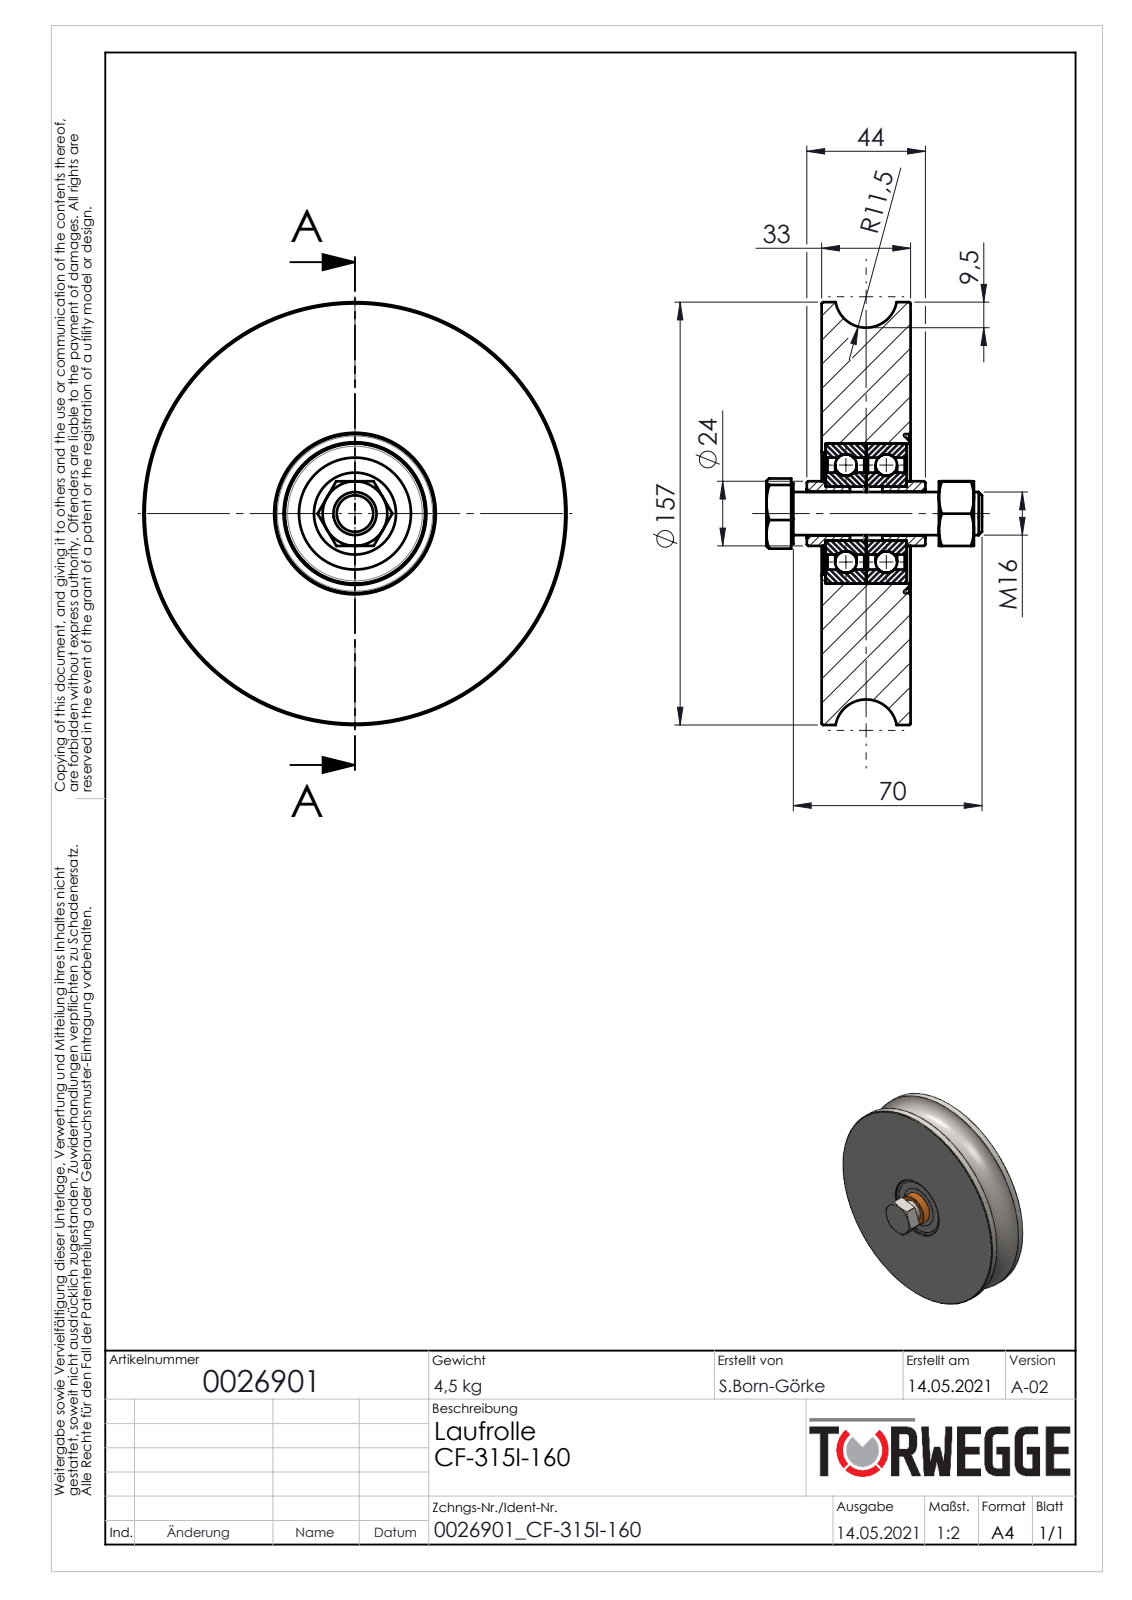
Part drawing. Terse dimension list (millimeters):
name: 0026901
written by: SolidWorks 2020 (AUTOMOTIVE_DESIGN)
unit: mm
bodies: 15 solids, 247 faces (44 planar, 78 cylindrical, 125 other)
size: 157 × 157 × 80
volume: 566 723 mm³; area: 102 681 mm²
holes: 1× ⌀13.83, 1× ⌀16.2, 1× ⌀20, 1× ⌀30.44, 1× ⌀41.56, 1× ⌀45, 1× ⌀59
bosses: 1× ⌀157, 1× ⌀52, 1× ⌀24, 1× ⌀22.5, 1× ⌀16
face distances: 33, 15, 16.5, 1.5, 31.5, 0.7, 14.3, 14.8, 0.5, 14.1
